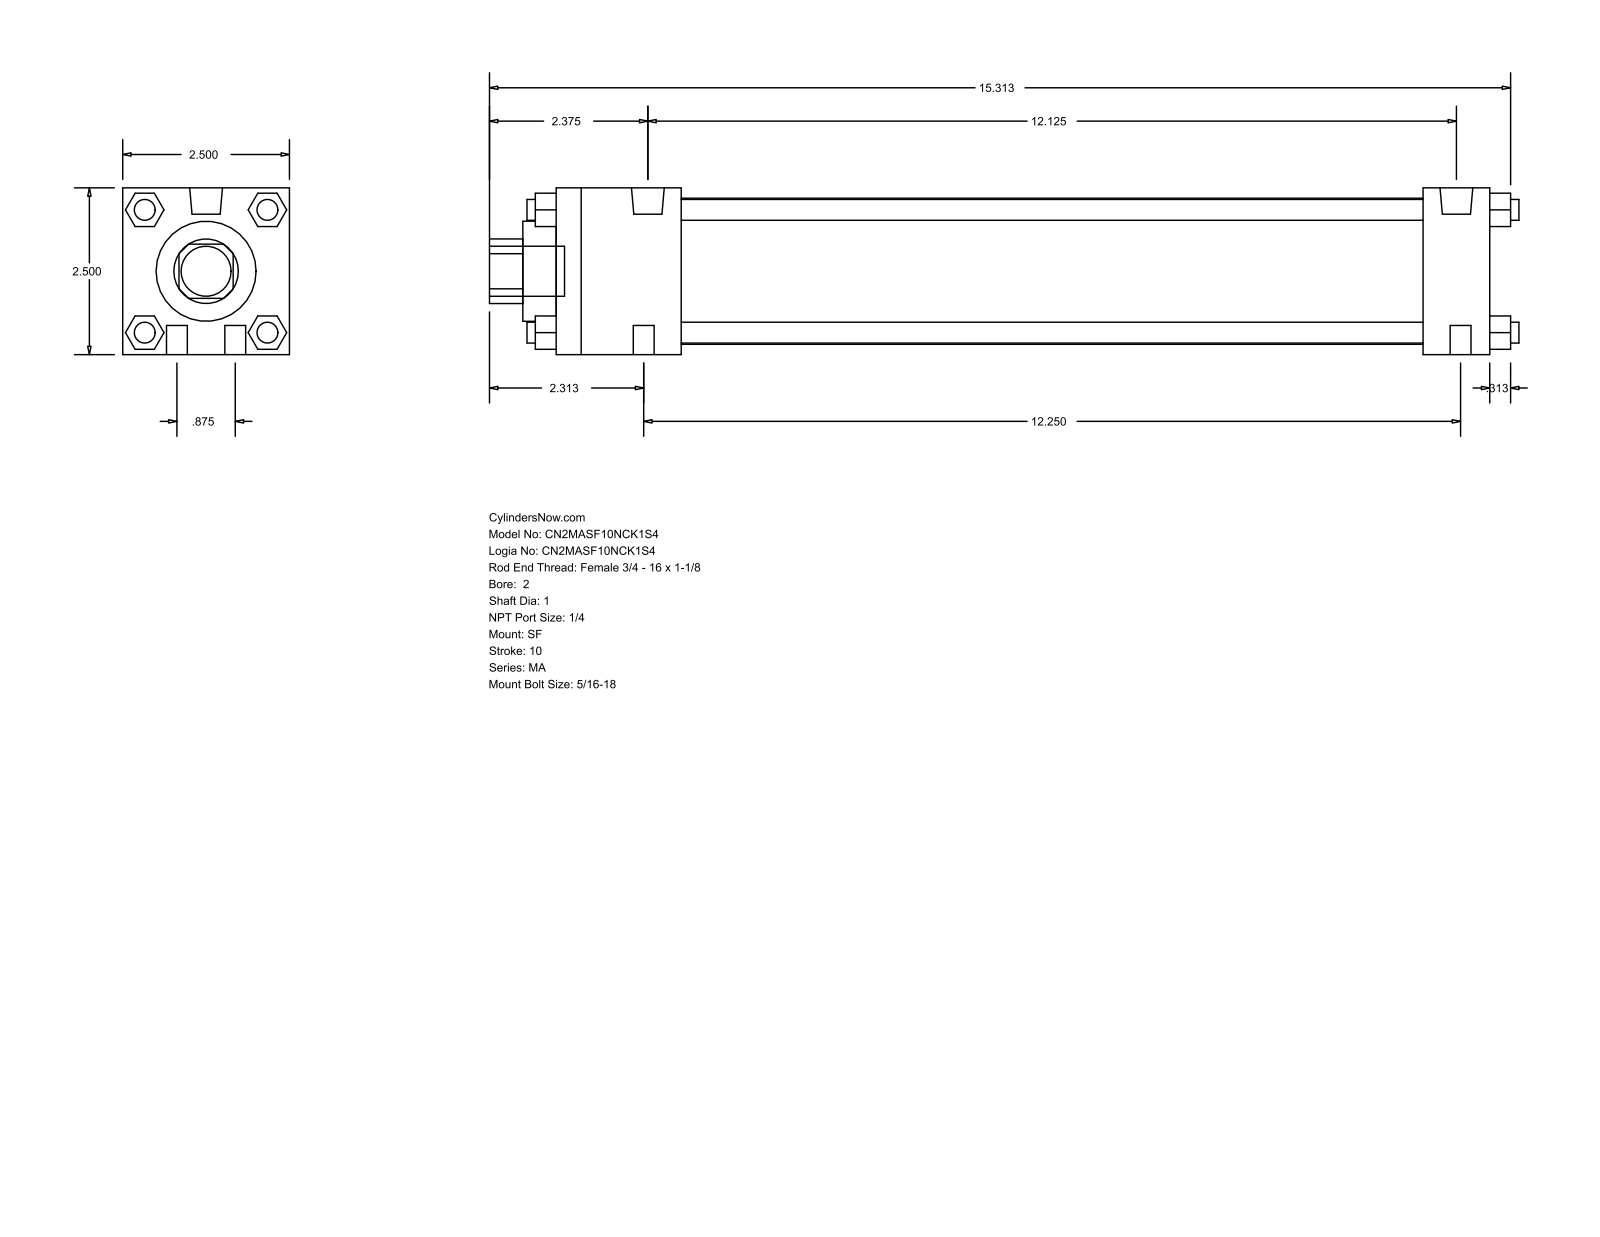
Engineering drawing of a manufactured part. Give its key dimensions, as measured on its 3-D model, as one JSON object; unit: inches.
{"part_name": "MA_SF__0200_1", "step_written_by": "GSSL Pune (CONFIG_CONTROL_DESIGN)", "units": "inches", "bodies": {"solids": 0, "faces": 124, "planar": 94, "cylindrical": 30, "other": 0}, "overall_size": [15.437, 2.5, 2.5], "round_holes": [[1, 1], [1.5, 1], [2.19, 1]], "round_bosses_or_shafts": [[0.313, 10], [0.492, 2], [0.75, 1]], "partial_cylinders_radius": [[0.484, 1]], "face_to_face_distances": [2.5, 14, 0.5, 1, 13, 1.875, 11.125, 12.125, 0.92, 1.593]}
